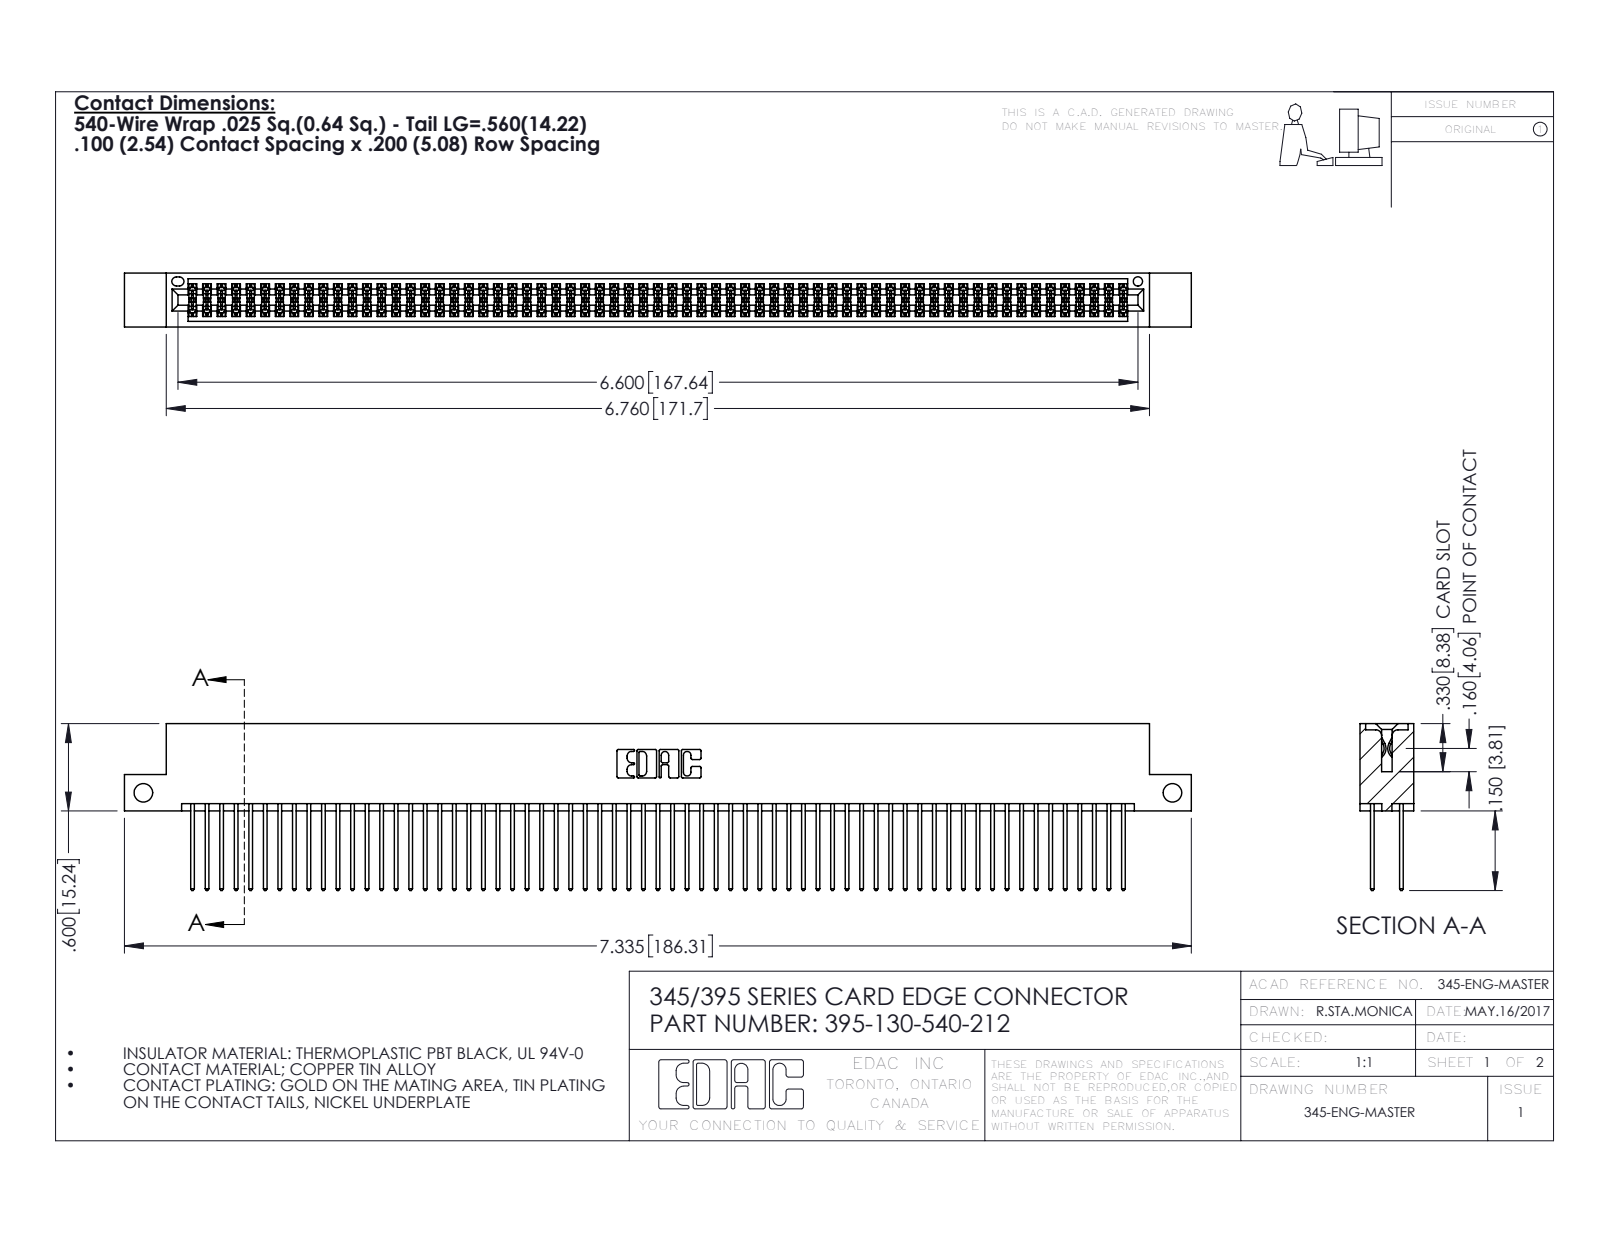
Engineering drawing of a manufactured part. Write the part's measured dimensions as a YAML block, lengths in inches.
part_name: "345 Part_Flush Mounting Lugs - Side Mount; 395-130-540-212; 345-292-001_345-293-140"
step_written_by: "SolidWorks 2016 (CONFIG_CONTROL_DESIGN)"
units: inches
bodies: {solids: 131, faces: 6626, planar: 4370, cylindrical: 2256, other: 0}
overall_size: [7.335, 1.147, 0.37]
volume: 1.142
surface_area: 46.91
round_holes:
  - {diameter: 0.128, count: 2}
  - {diameter: 0.064, count: 1}
partial_cylinders:
  - {radius: 0.006, count: 195}
  - {radius: 0.01, count: 130}
  - {radius: 0.01, count: 22}
  - {radius: 0.007, count: 6}
  - {radius: 0.031, count: 6}
  - {radius: 0.026, count: 3}
  - {radius: 0.014, count: 2}
  - {radius: 0.019, count: 2}
face_to_face_distances: [0.298, 0.072, 0.2, 0.098, 0.272, 0.025, 0.225, 0.37, 0.175, 0.149]
hole_center_spacings: [7.075]
